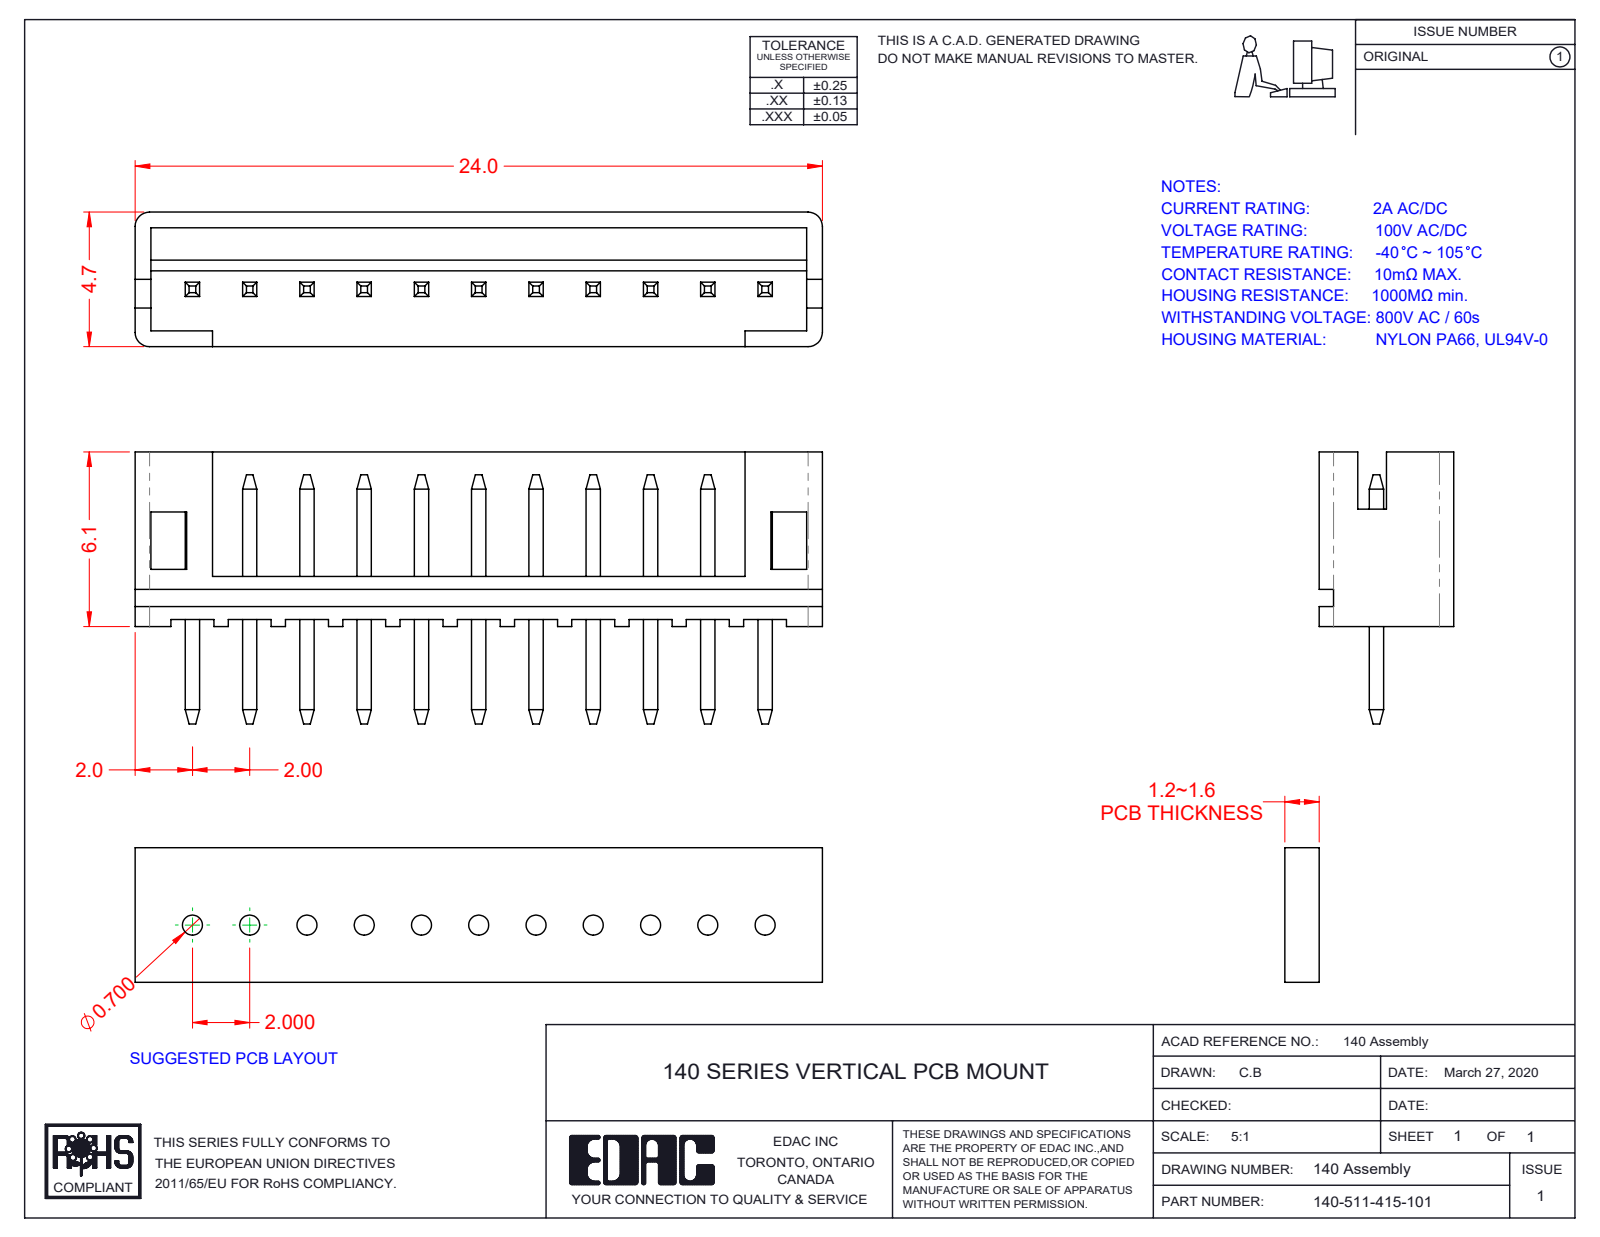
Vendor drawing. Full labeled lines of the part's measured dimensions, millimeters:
Part name (STEP PRODUCT): 140-511-415-101; V LI Contact_Str; V LI Housing_511
STEP written by: SolidWorks 2020 (CONFIG_CONTROL_DESIGN)
Units: millimetres
Bodies: 12 solids, 282 faces (276 planar, 6 cylindrical, 0 other)
Overall size (bounding box): 24 × 9.5 × 4.7
Volume: 251 mm³ · Surface area: 918 mm²
Partial cylindrical surfaces — rounded edges, fillets, slot ends (radius × count): R0.5 ×4
Main face-to-face distances: 0.55, 0.5, 1.75, 1.5, 2, 4, 2.95, 2.4, 2.45, 1.9
